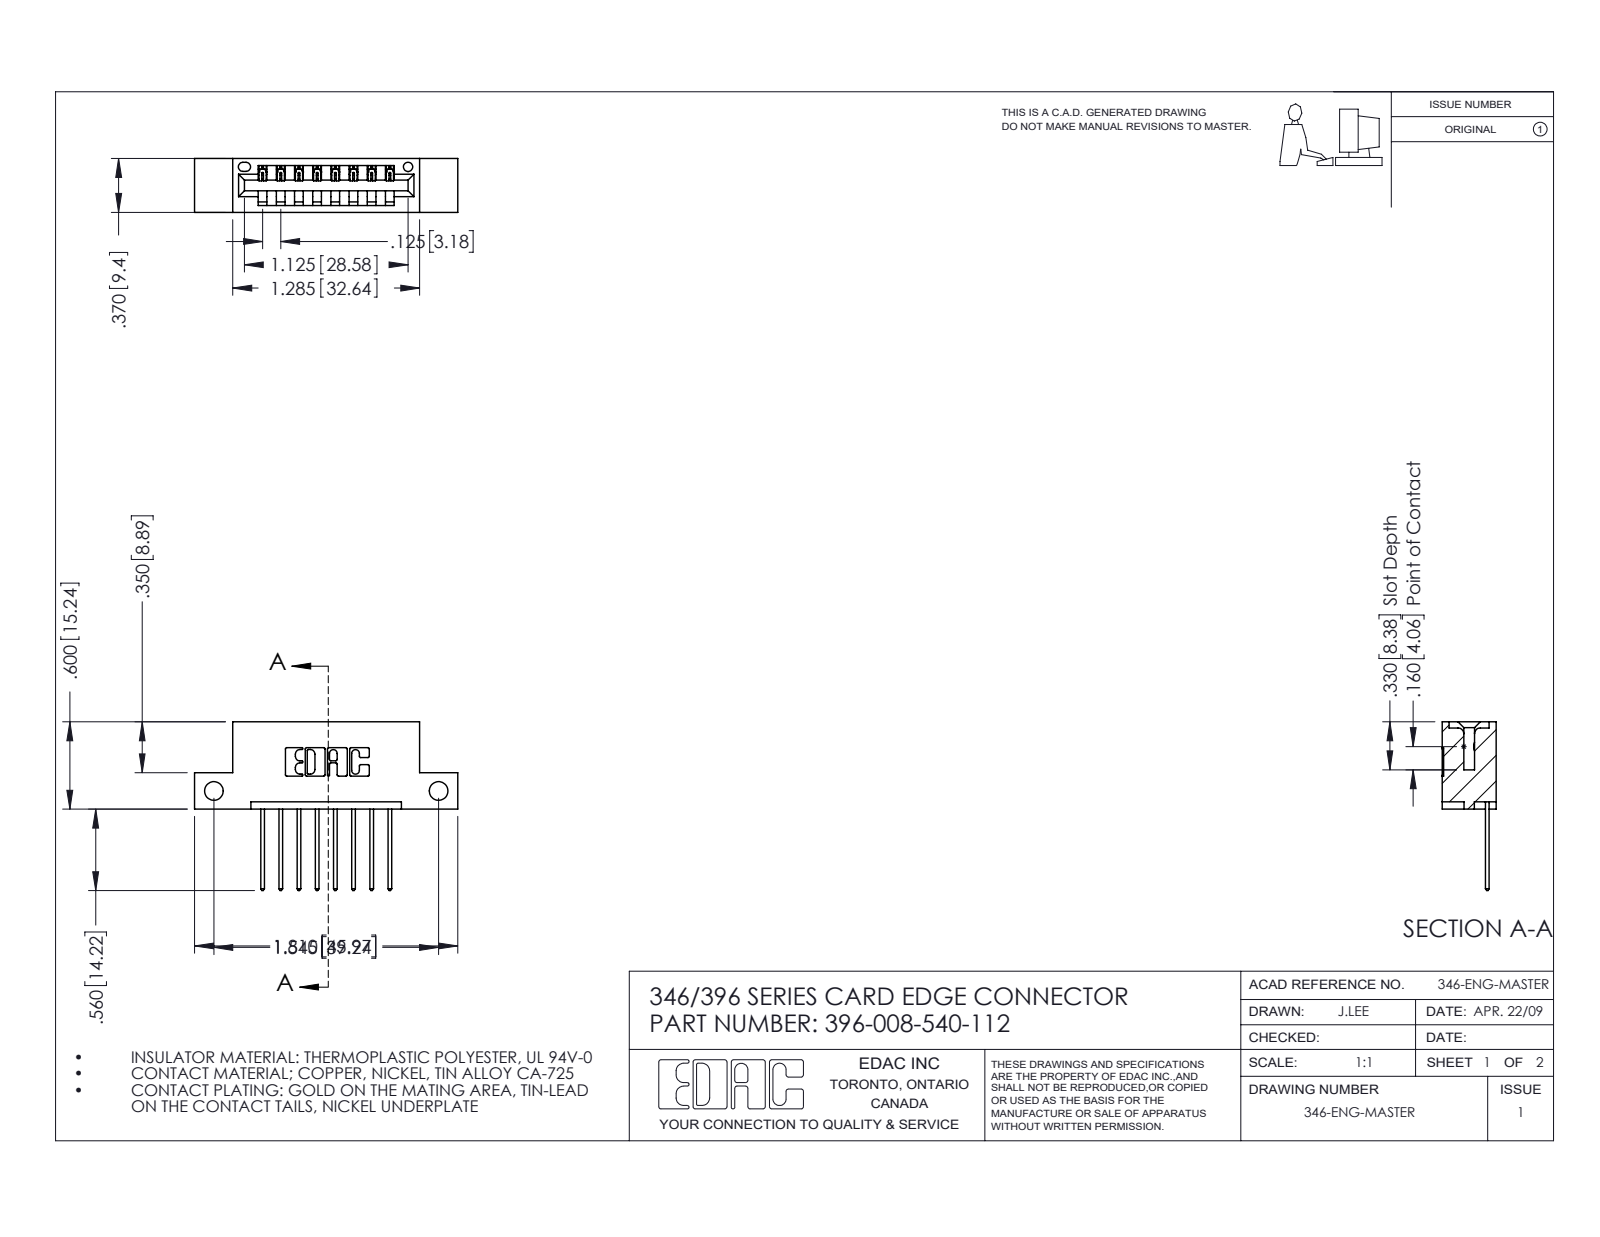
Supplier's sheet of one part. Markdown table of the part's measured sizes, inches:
| quantity | value |
| --- | --- |
| part name | 345-292-001_345-293-140; 346 Part_Flush Mounting Lugs - Side Mount; 396-008-540-112 |
| STEP written by | SolidWorks 2016 (CONFIG_CONTROL_DESIGN) |
| units | inches |
| bodies | 9 solids, 586 faces (396 planar, 190 cylindrical, 0 other) |
| overall size | 1.81 × 1.16 × 0.37 |
| volume | 0.25 in³ |
| surface area | 7.252 in² |
| round holes (diameter × count) | 0.128 × 2, 0.064 × 1 |
| partial cylindrical surfaces (radius × count) | 0.01 × 22, 0.006 × 16, 0.01 × 16, 0.007 × 6, 0.031 × 6, 0.026 × 3, 0.031 × 2, 0.04 × 2 |
| main face-to-face distances | 0.25, 0.048, 0.322, 0.37, 0.072, 0.298, 0.025, 0.5, 0.148, 0.222 |
| hole center spacings | 1.545 |
